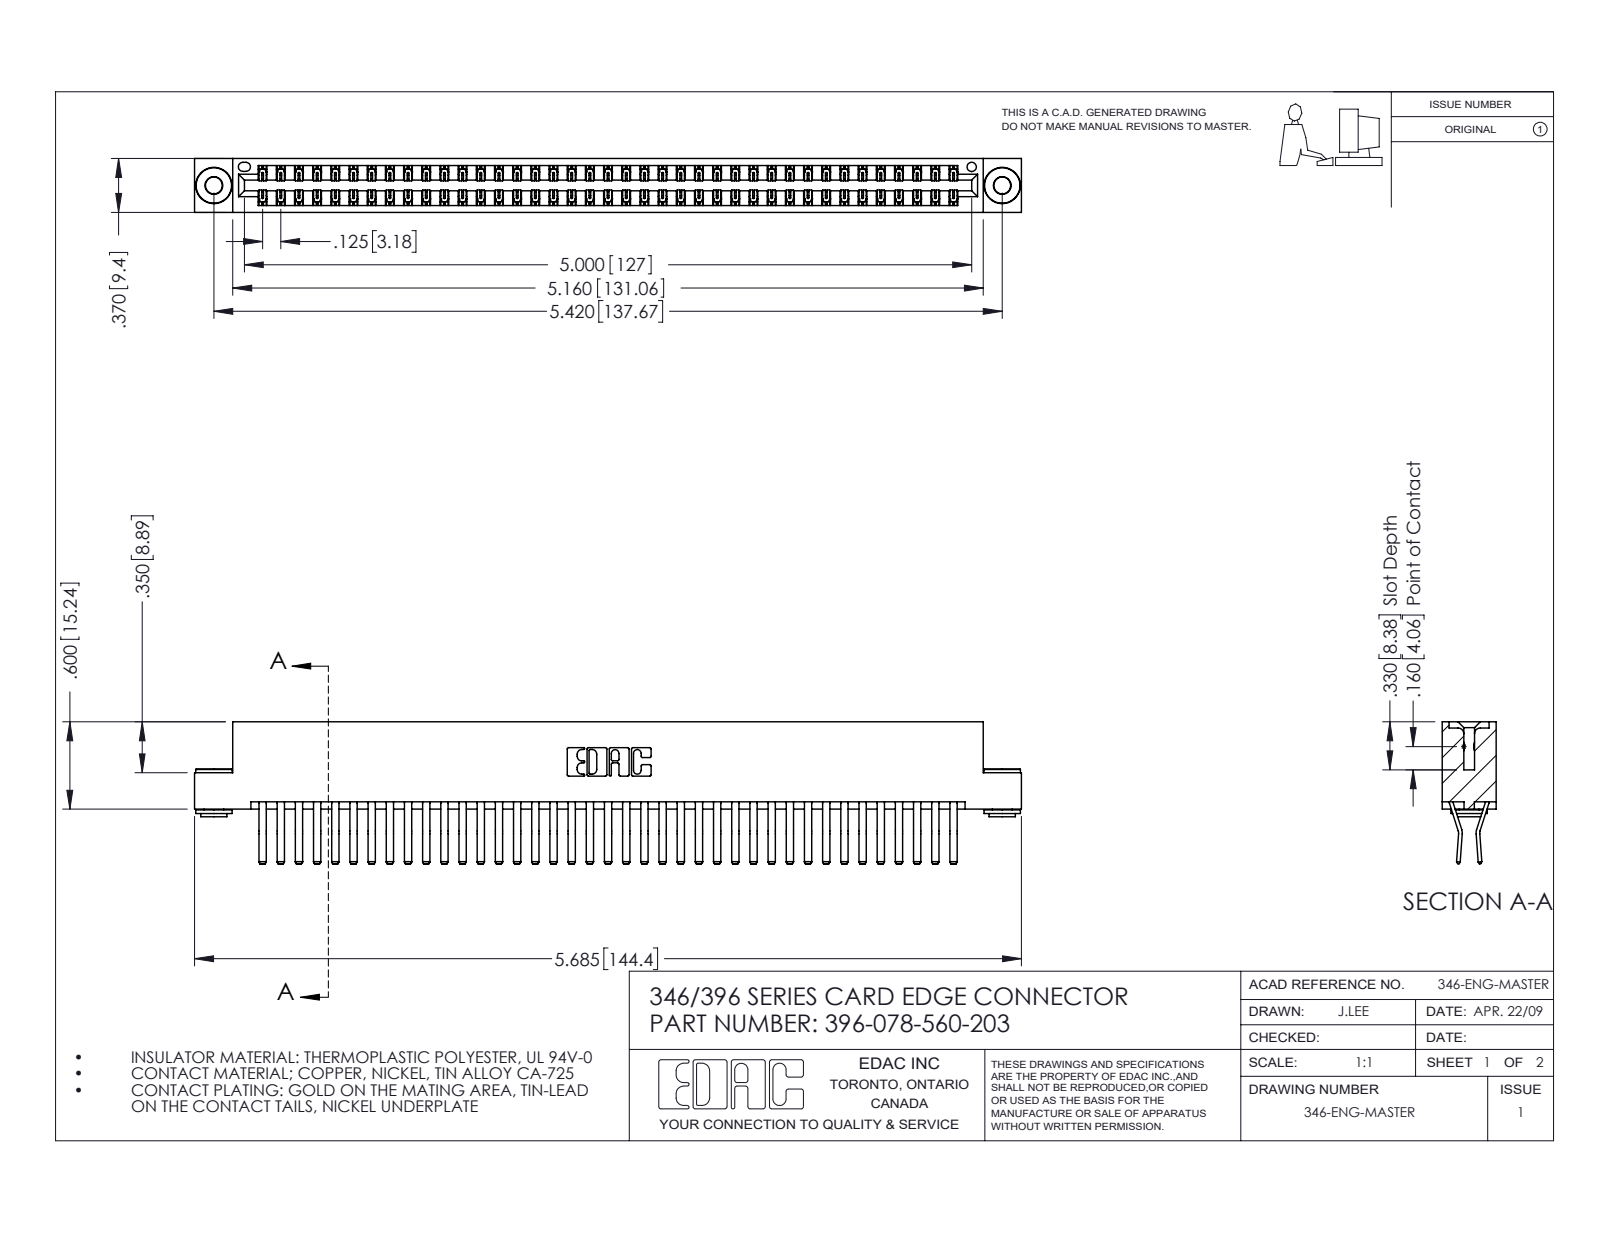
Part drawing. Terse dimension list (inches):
name: 345-250-002_345-250-002-102; 396-078-560-203; 345-292-001_560 Tail; 346 Part_Flush Mounting Lugs - 0.156 Dia-TH
written by: SolidWorks 2016 (CONFIG_CONTROL_DESIGN)
unit: in
bodies: 81 solids, 4372 faces (2816 planar, 1548 cylindrical, 8 other)
size: 5.685 × 0.975 × 0.37
volume: 0.89 in³; area: 33.45 in²
holes: 2× ⌀0.116, 2× ⌀0.156, 1× ⌀0.064
bosses: 2× ⌀0.25, 2× ⌀0.18, 2× ⌀0.136
rounds: 117× R0.006, 22× R0.01, 6× R0.007, 6× R0.031, 3× R0.026, 2× R0.01, 2× R0.014, 2× R0.022
face distances: 0.048, 0.322, 0.37, 0.025, 0.25, 0.072, 0.298, 0.275, 0.148, 0.222
hole spacings: 0.246, 5.211, 5.42
